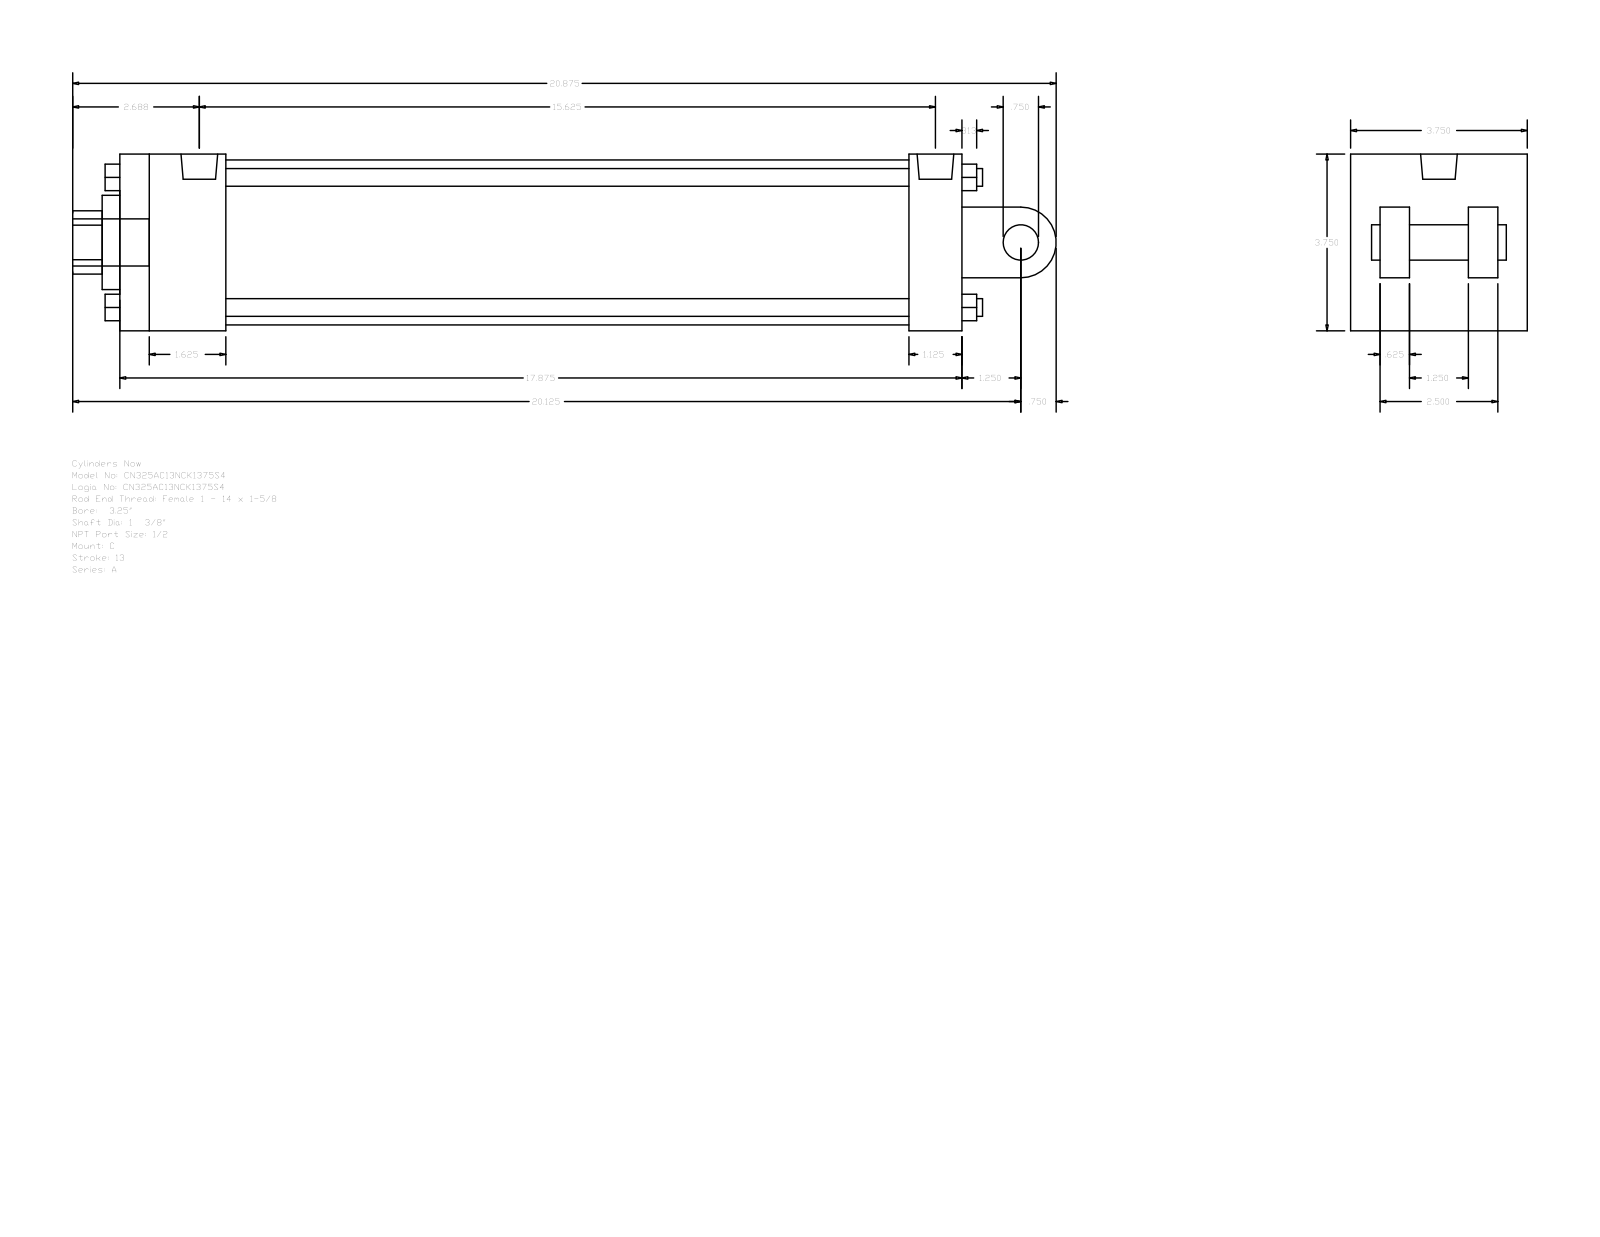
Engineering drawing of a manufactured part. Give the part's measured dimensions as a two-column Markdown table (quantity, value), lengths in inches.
| quantity | value |
| --- | --- |
| part name | A_C__0325_1.375 |
| STEP written by | GSSL Pune (CONFIG_CONTROL_DESIGN) |
| units | inches |
| bodies | 0 solids, 135 faces (102 planar, 33 cylindrical, 0 other) |
| overall size | 20.875 × 3.75 × 3.75 |
| round holes (diameter × count) | 0.344 × 2, 0.778 × 1, 1.375 × 1, 2 × 1, 3.5 × 1 |
| round bosses / shafts (diameter × count) | 0.375 × 4, 0.344 × 2, 1 × 1, 0.778 × 1, 0.75 × 1 |
| partial cylindrical surfaces (radius × count) | 0.672 × 1, 0.75 × 1 |
| main face-to-face distances | 3.75, 0.625, 17.875, 2.5, 2.625, 1.125, 3.125, 1.25, 1.875, 16.75 |
| hole center spacings | 0.125 |
